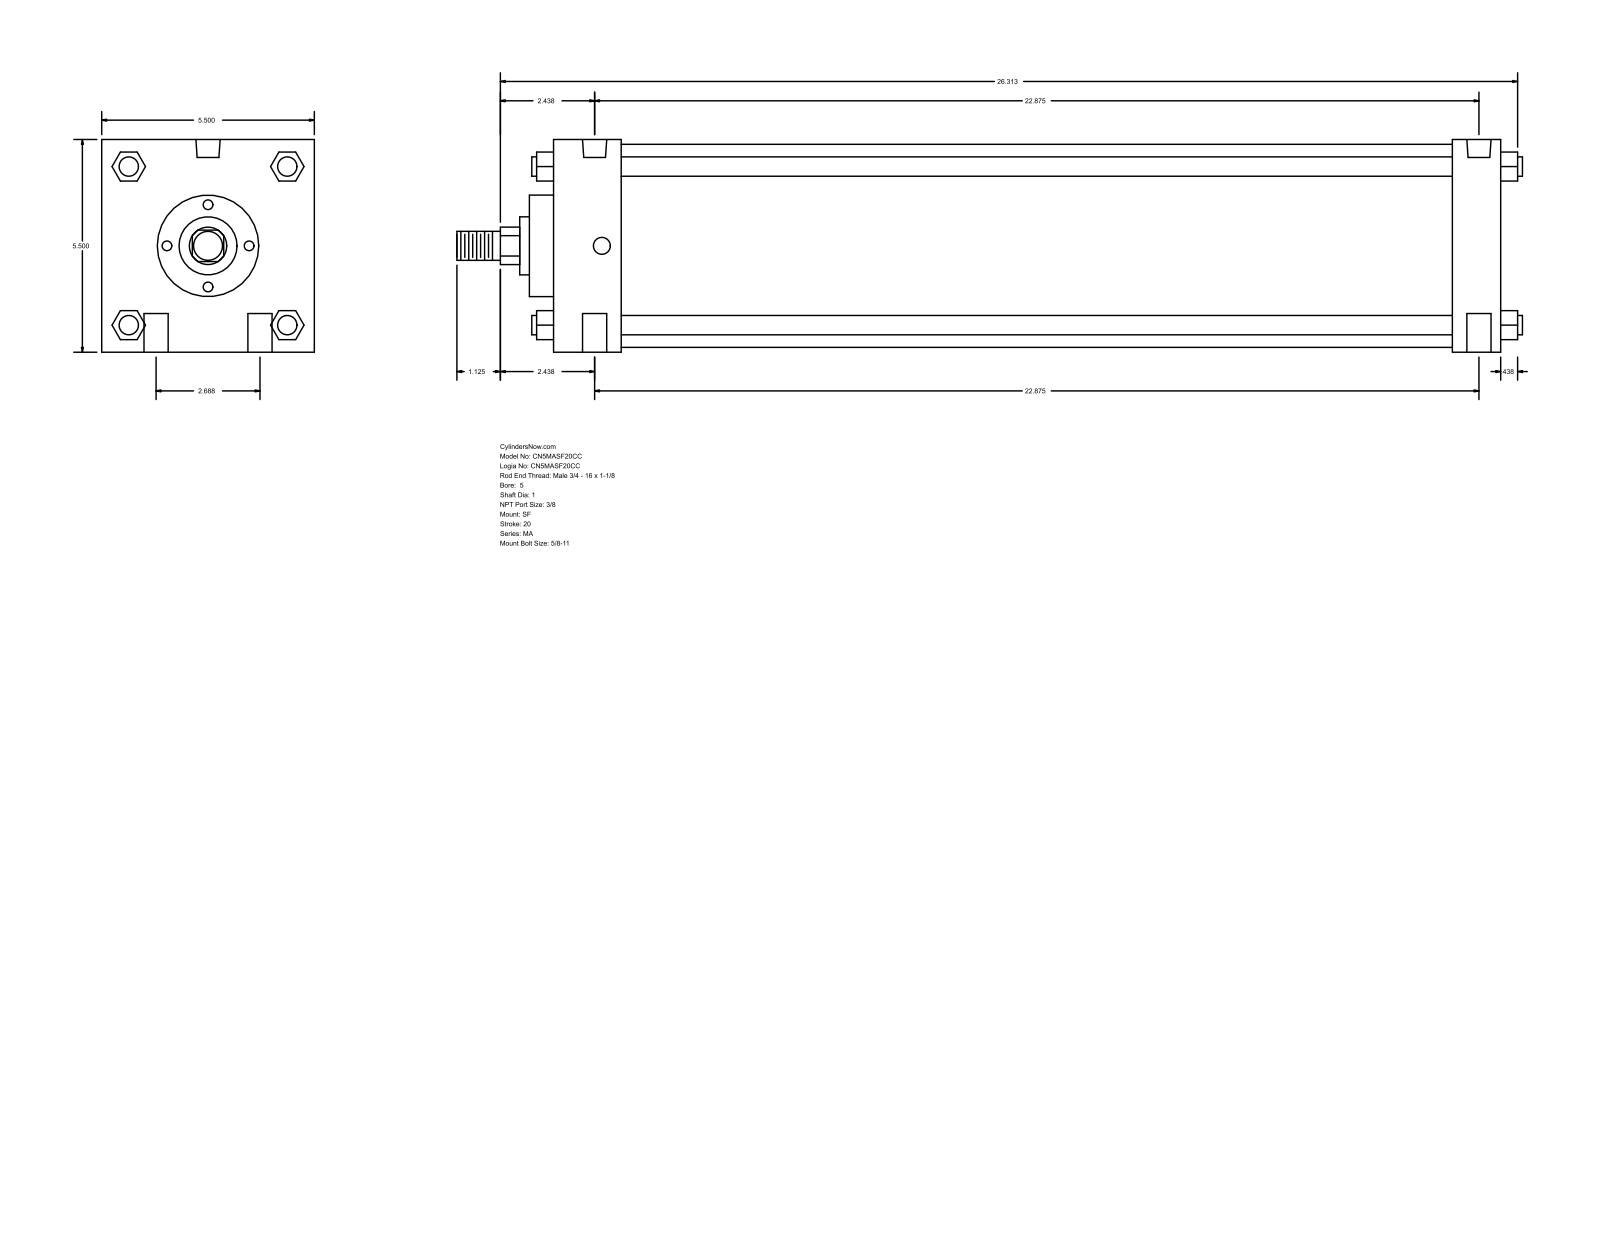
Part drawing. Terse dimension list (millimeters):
name: MA_SF__0500_1
written by: GSSL Pune (CONFIG_CONTROL_DESIGN)
unit: mm
bodies: 0 solids, 126 faces (95 planar, 31 cylindrical, 0 other)
size: 700.09 × 139.7 × 139.7
holes: 4× ⌀15.88, 2× ⌀11.11, 2× ⌀15.93
bosses: 4× ⌀12.7, 1× ⌀133.35, 1× ⌀66.67, 1× ⌀38.1, 1× ⌀25.4, 1× ⌀19.05
rounds: 1× R12.29
face distances: 139.7, 622.31, 44.46, 590.56, 546.1, 577.85, 31.75, 15.87, 60.33, 606.43
hole spacings: 34.13, 582.03, 581.03, 68.26, 585.03, 571.5
